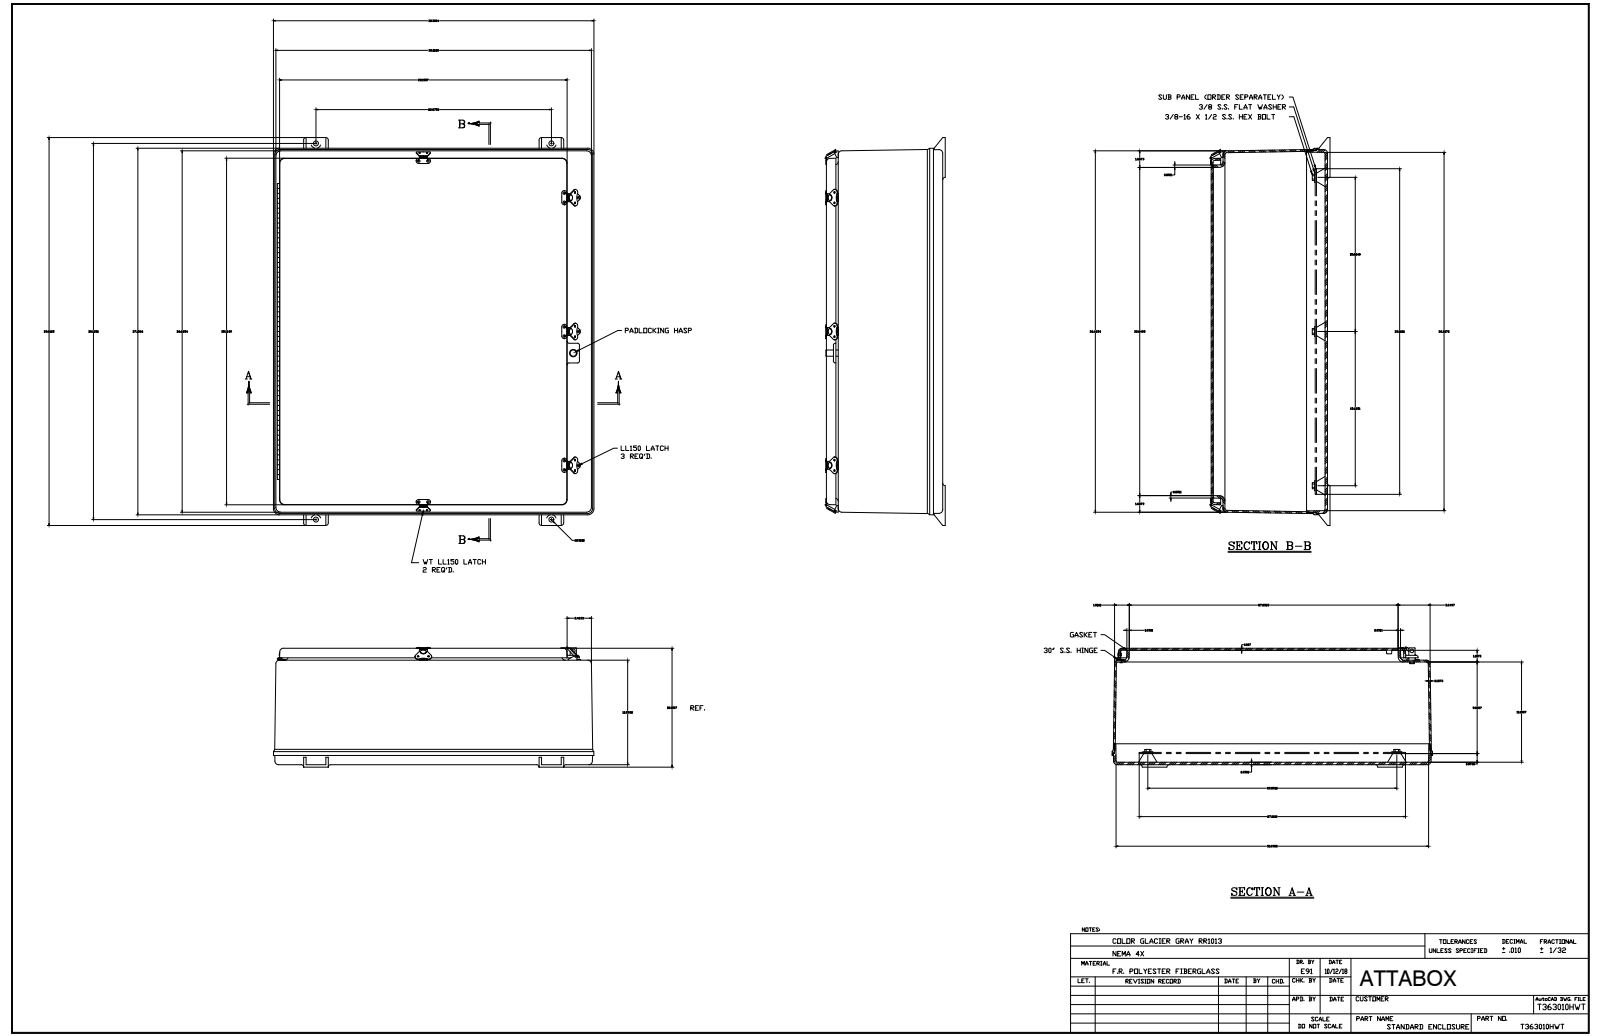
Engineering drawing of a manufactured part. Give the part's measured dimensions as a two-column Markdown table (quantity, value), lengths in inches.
| quantity | value |
| --- | --- |
| part name | T363010HWT |
| STEP written by | SolidWorks 2018 (AUTOMOTIVE_DESIGN) |
| units | inches |
| bodies | 63 solids, 1821 faces (693 planar, 736 cylindrical, 392 other) |
| overall size | 39.313 × 32.5 × 12.397 |
| volume | 875.7 in³ |
| surface area | 8 812 in² |
| round holes (diameter × count) | 0.13 × 36, 0.063 × 20, 0.138 × 10, 0.187 × 10, 0.065 × 7, 0.563 × 4, 0.156 × 3, 0.135 × 2, 0.433 × 2, 0.51 × 2, 0.51 × 2, 0.065 × 1 |
| round bosses / shafts (diameter × count) | 0.14 × 20, 0.297 × 8, 0.5 × 5, 0.2 × 3, 0.135 × 2, 0.25 × 1, 0.201 × 1, 0.135 × 1 |
| partial cylindrical surfaces (radius × count) | 0.01 × 127, 0.25 × 24, 0.03 × 20, 0.188 × 18, 0.375 × 13, 0.312 × 12, 0.5 × 12, 0.313 × 11 |
| main face-to-face distances | 0.25, 11.813, 11.563, 11.624, 11.374, 0.188, 0.187, 0.188, 10.594, 1.219 |
| hole center spacings | 9.5, 19.5, 13.563, 1, 1.526, 10, 29, 3.474 |
